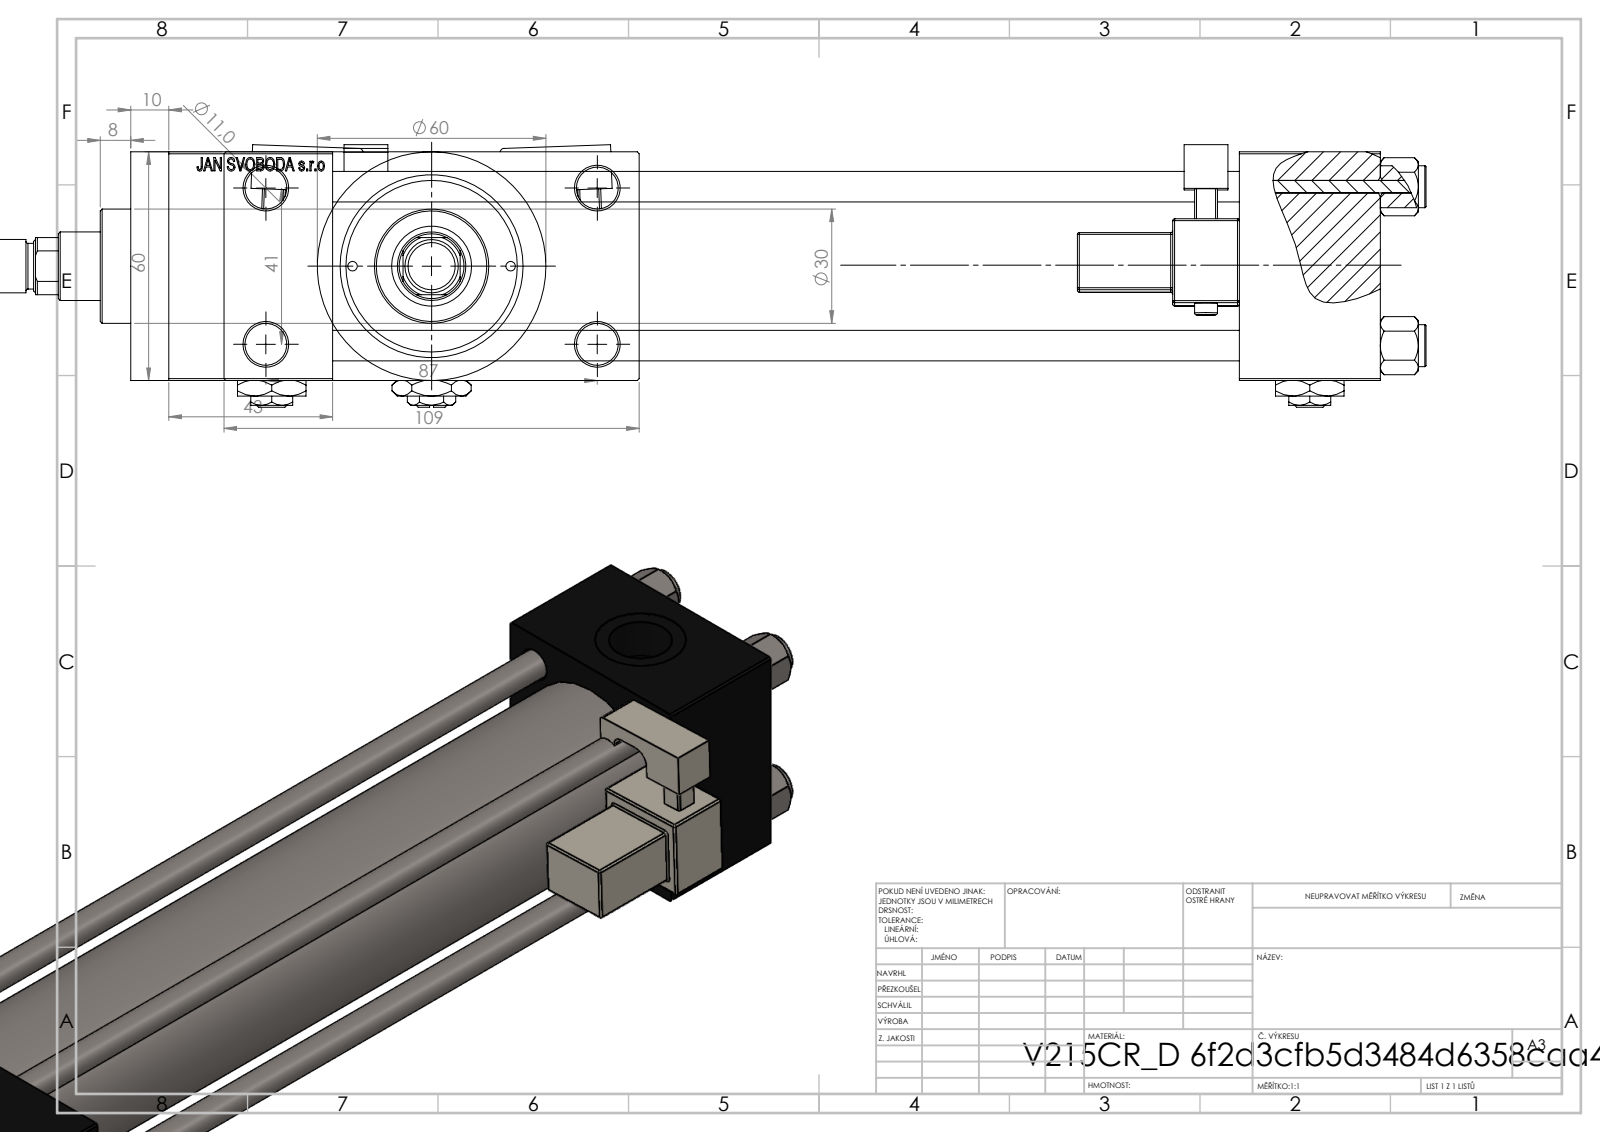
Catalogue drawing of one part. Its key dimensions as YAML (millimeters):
part_name: "V215CR_MSU; NUT_M5_D; V215_VC_A; V215CR_VCP_D (+4 more)"
step_written_by: "SolidWorks 2019 (CONFIG_CONTROL_DESIGN)"
units: millimeters
bodies: {solids: 16, faces: 1382, planar: 610, cylindrical: 168, other: 604}
overall_size: [383, 109, 68.9]
volume: 713832
surface_area: 213992
round_holes:
  - {diameter: 8, count: 4}
  - {diameter: 11, count: 4}
  - {diameter: 2.5, count: 2}
  - {diameter: 7, count: 2}
  - {diameter: 16.66, count: 2}
  - {diameter: 24, count: 2}
  - {diameter: 8.5, count: 1}
  - {diameter: 18, count: 1}
  - {diameter: 21, count: 1}
  - {diameter: 31, count: 1}
  - {diameter: 40, count: 1}
  - {diameter: 45, count: 1}
round_bosses_or_shafts:
  - {diameter: 11, count: 4}
  - {diameter: 6, count: 2}
  - {diameter: 60, count: 1}
  - {diameter: 46, count: 1}
  - {diameter: 30, count: 1}
  - {diameter: 14, count: 1}
  - {diameter: 12, count: 1}
partial_cylinders:
  - {radius: 0.5, count: 48}
  - {radius: 1, count: 2}
  - {radius: 2.5, count: 2}
  - {radius: 4, count: 2}
  - {radius: 8.5, count: 1}
face_to_face_distances: [60, 238, 24.5, 84.5, 37, 275, 43, 318, 281, 109]
hole_center_spacings: [20.85, 22.65, 29.49, 30.62, 41.7, 46.53, 47.15, 48.09]
